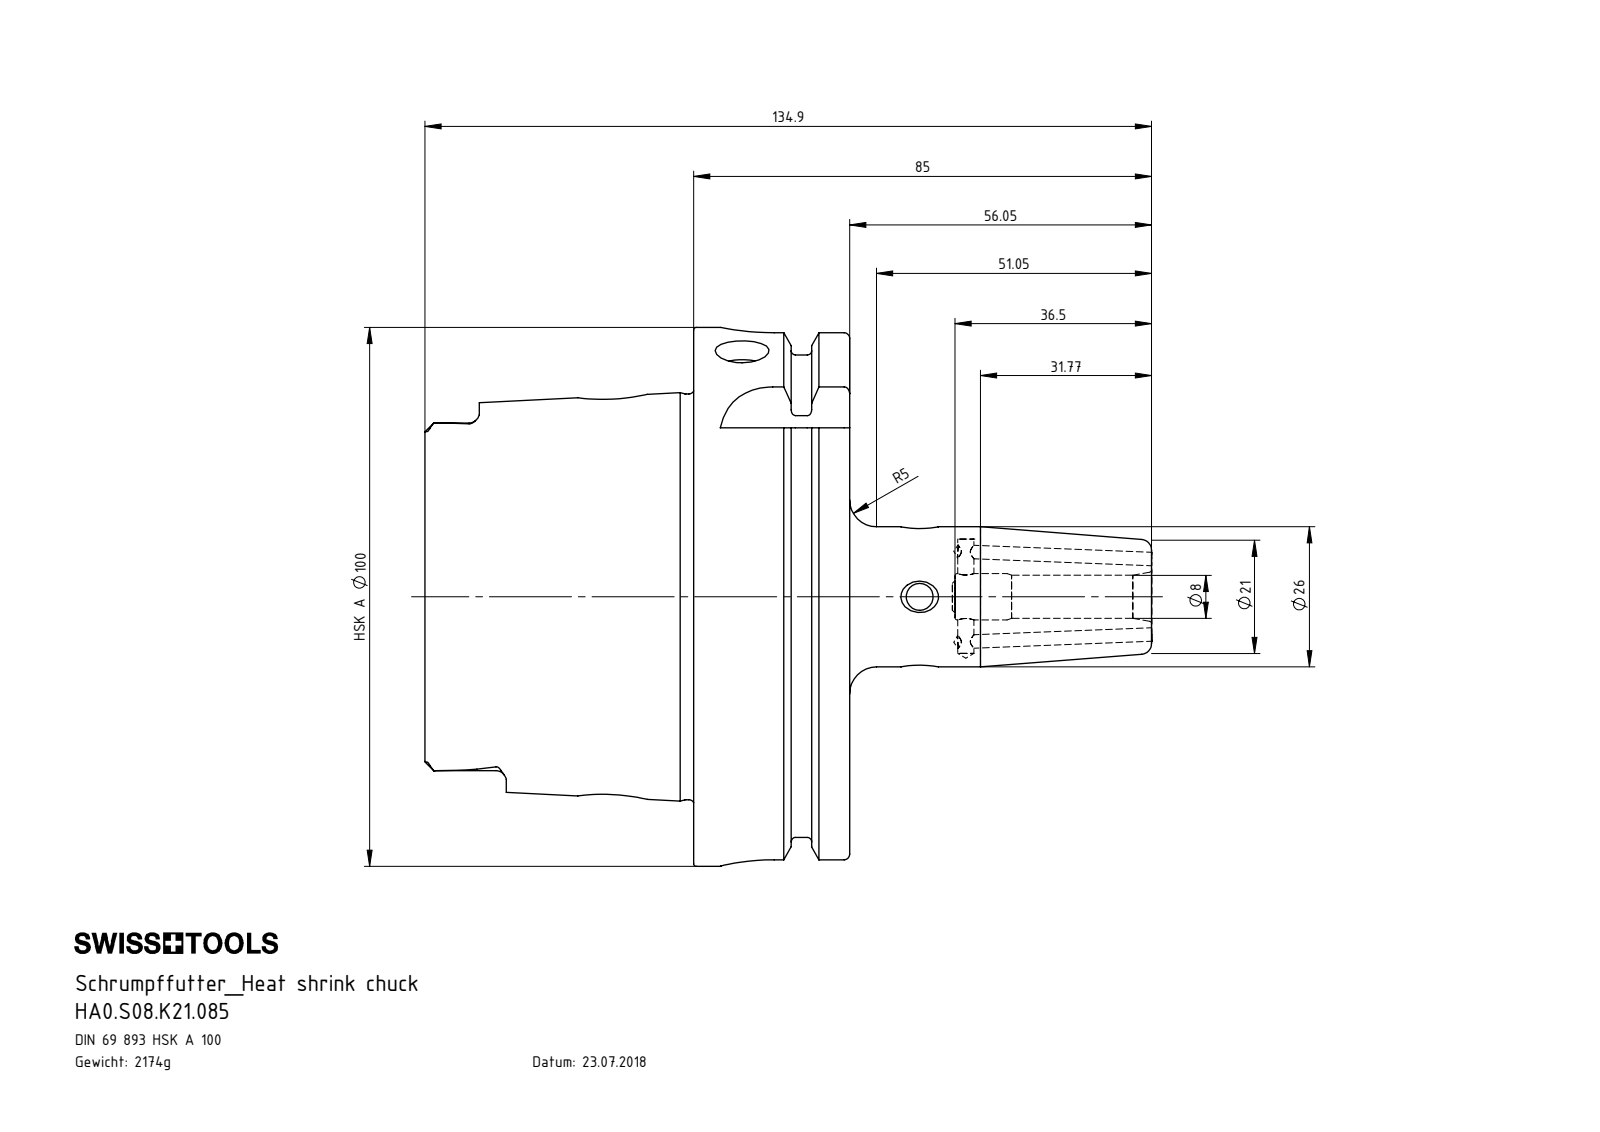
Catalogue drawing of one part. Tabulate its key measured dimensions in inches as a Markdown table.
| quantity | value |
| --- | --- |
| part name | HA0.S08.K21.085; HA0-S08.K21.085_C_Fertigbearbeitung; ERU-AN2.K01.016_A; ERU-CJ2.001.006 |
| STEP written by | SolidWorks 2017 (AUTOMOTIVE_DESIGN) |
| units | inches |
| bodies | 4 solids, 299 faces (95 planar, 86 cylindrical, 118 other) |
| overall size | 5.314 × 3.937 × 3.937 |
| volume | 16.9 in³ |
| surface area | 87.99 in² |
| round holes (diameter × count) | 0.197 × 3, 0.394 × 3, 0.098 × 2, 0.118 × 2, 0.268 × 1, 0.315 × 1, 0.339 × 1, 0.472 × 1, 0.886 × 1, 1.024 × 1, 2.087 × 1, 2.48 × 1 |
| round bosses / shafts (diameter × count) | 0.118 × 2, 3.937 × 1, 3.62 × 1, 2.963 × 1, 0.236 × 1 |
| partial cylindrical surfaces (radius × count) | 0.075 × 6, 0.192 × 4, 0.394 × 4 |
| main face-to-face distances | 1.14, 0.49, 0.65, 1.965, 2.455, 3.104, 3.079, 1.114, 0.624, 0.026 |
| hole center spacings | 0.337, 1.376, 2.242, 2.579 |
